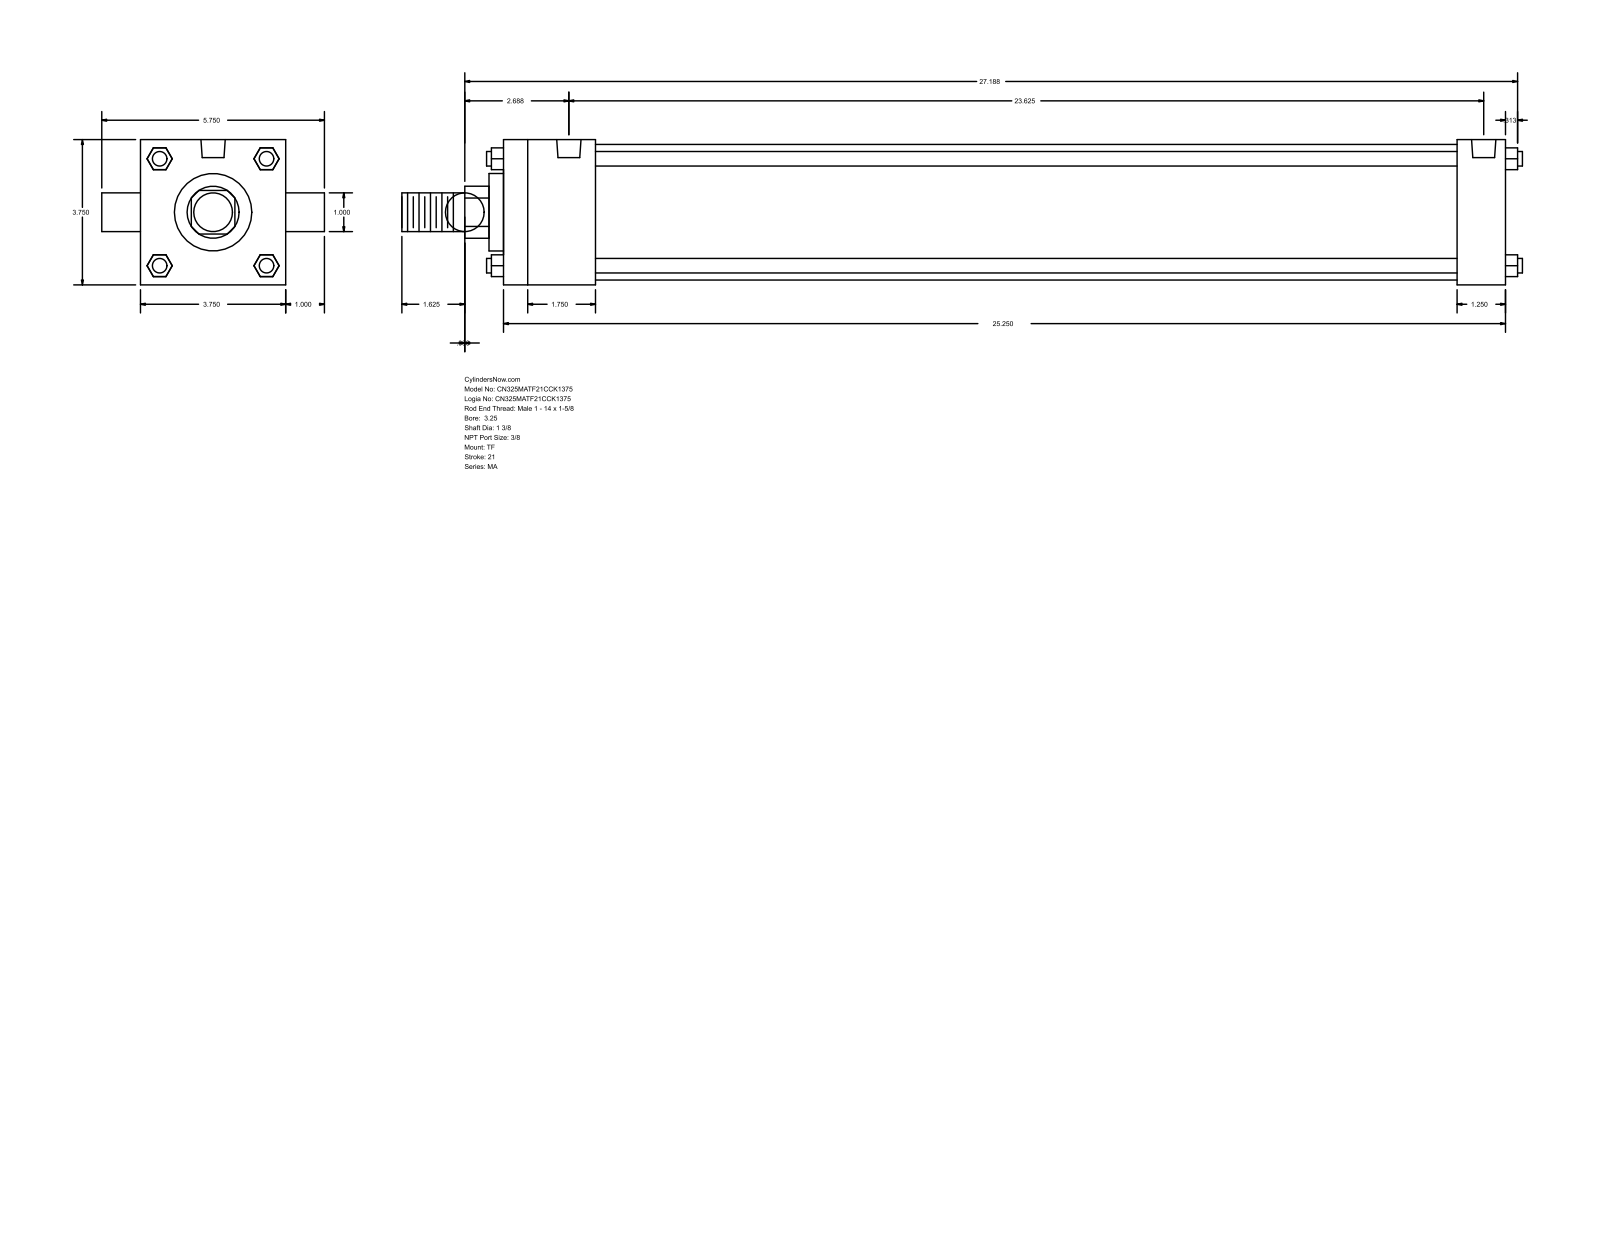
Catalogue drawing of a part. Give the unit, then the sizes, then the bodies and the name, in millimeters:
Units: millimetres
Overall size (bounding box): 735.01 × 146.05 × 95.25
Round holes (diameter × count): ⌀11.11 ×3, ⌀15.93 ×2
Round bosses / shafts (diameter × count): ⌀9.53 ×4, ⌀25.4 ×2, ⌀88.9 ×1, ⌀50.8 ×1, ⌀34.92 ×1
Partial cylindrical surfaces — rounded edges, fillets, slot ends (radius × count): R17.06 ×1
Main face-to-face distances: 95.24, 657.22, 60.32, 625.48, 565.16, 596.9, 31.74, 9.52, 69.84, 635
Hole centre spacings: 4.76, 4.77, 590.55, 595.31, 595.32, 600.08
Bodies: 0 solids, 120 faces (92 planar, 28 cylindrical, 0 other)
Part name (STEP PRODUCT): MA_TF__0325_1.375
STEP written by: GSSL Pune (CONFIG_CONTROL_DESIGN)
